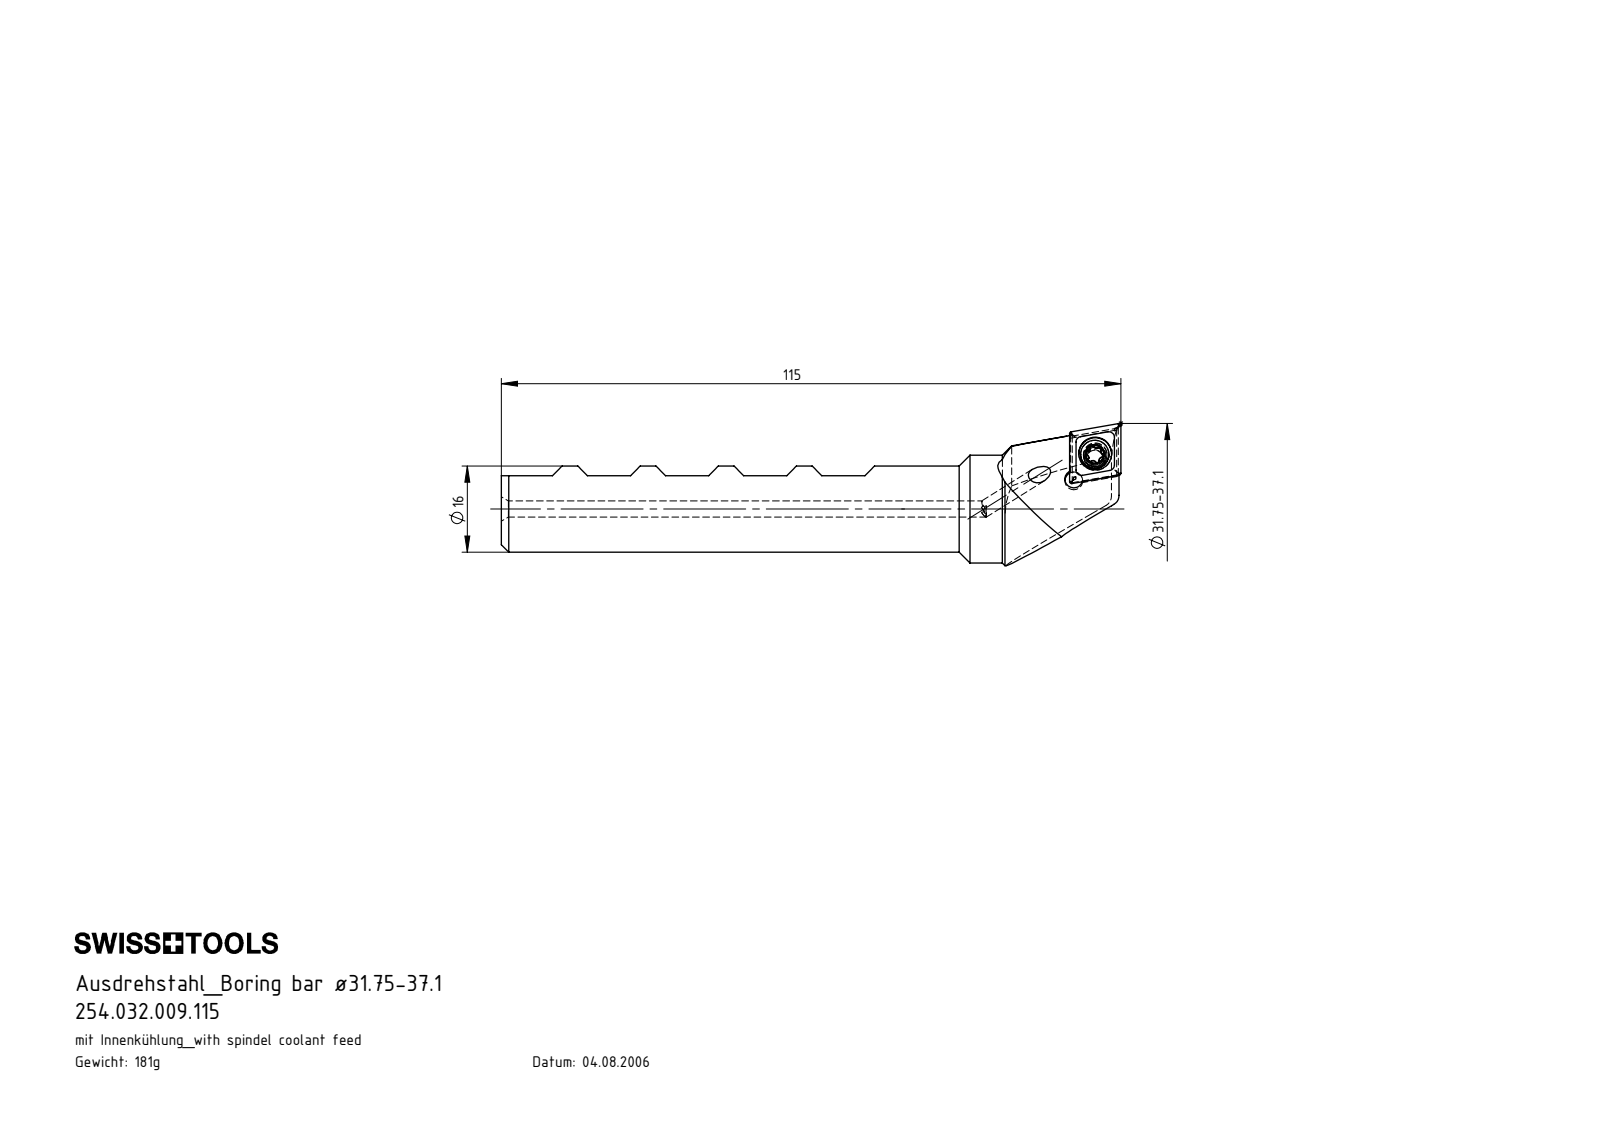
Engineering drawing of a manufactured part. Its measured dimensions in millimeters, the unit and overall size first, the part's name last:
Units: millimetres
Overall size (bounding box): 115 × 26.38 × 21.89
Round holes (diameter × count): ⌀3 ×2, ⌀3.3 ×2, ⌀4.4 ×1, ⌀6.1 ×1
Round bosses / shafts (diameter × count): ⌀20 ×1, ⌀16 ×1, ⌀5.25 ×1, ⌀4 ×1
Partial cylindrical surfaces — rounded edges, fillets, slot ends (radius × count): R0.34 ×6, R0.59 ×6, R2 ×1, R10.5 ×1, R12 ×1
Main face-to-face distances: 7.91, 10.25, 20.5, 30.76, 20.51, 11.68, 3.77, 11.88, 3.97, 30.75
Hole centre spacings: 6.07, 6.2
Volume: 23 042 mm³ · Surface area: 7 978 mm²
Bodies: 3 solids, 116 faces (45 planar, 26 cylindrical, 45 other)
Part name (STEP PRODUCT): WCB-ER2.001.009_A; CCMT09T304; B32-WCB.K11.115_A; B32.WCB.K11.115
STEP written by: SolidWorks 2017 (AUTOMOTIVE_DESIGN)
